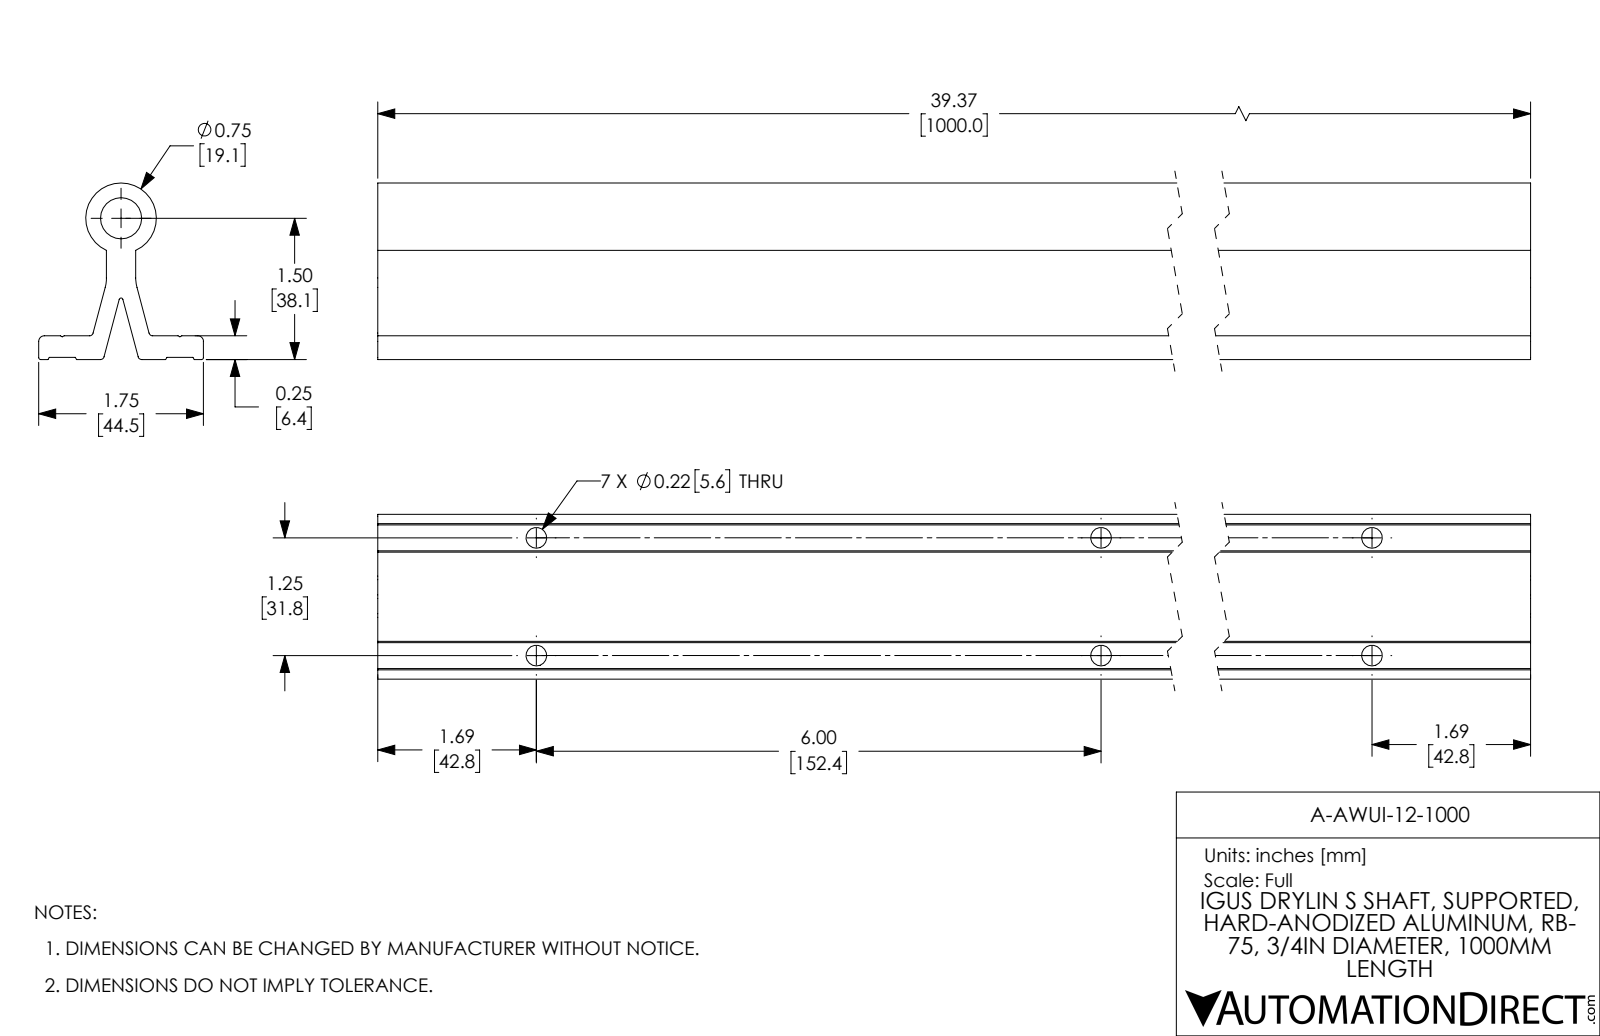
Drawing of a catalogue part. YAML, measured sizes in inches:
part_name: "A-AWUI-12-1000"
step_written_by: "SolidWorks 2017 (AUTOMOTIVE_DESIGN)"
units: inches
bodies: {solids: 1, faces: 98, planar: 56, cylindrical: 42, other: 0}
overall_size: [39.37, 1.875, 1.75]
volume: 37.01
surface_area: 381.4
round_holes:
  - {diameter: 0.22, count: 14}
  - {diameter: 0.437, count: 1}
round_bosses_or_shafts:
  - {diameter: 0.75, count: 1}
partial_cylinders:
  - {radius: 0.039, count: 4}
  - {radius: 0.02, count: 3}
  - {radius: 0.059, count: 2}
  - {radius: 0.394, count: 2}
face_to_face_distances: [0.177, 0.252, 0.024, 0.228, 0.311, 0.72, 1.031, 1.75, 1.03, 0.719]
hole_center_spacings: [6, 6.129, 12, 12.065, 18, 18.043, 1.25, 24]
